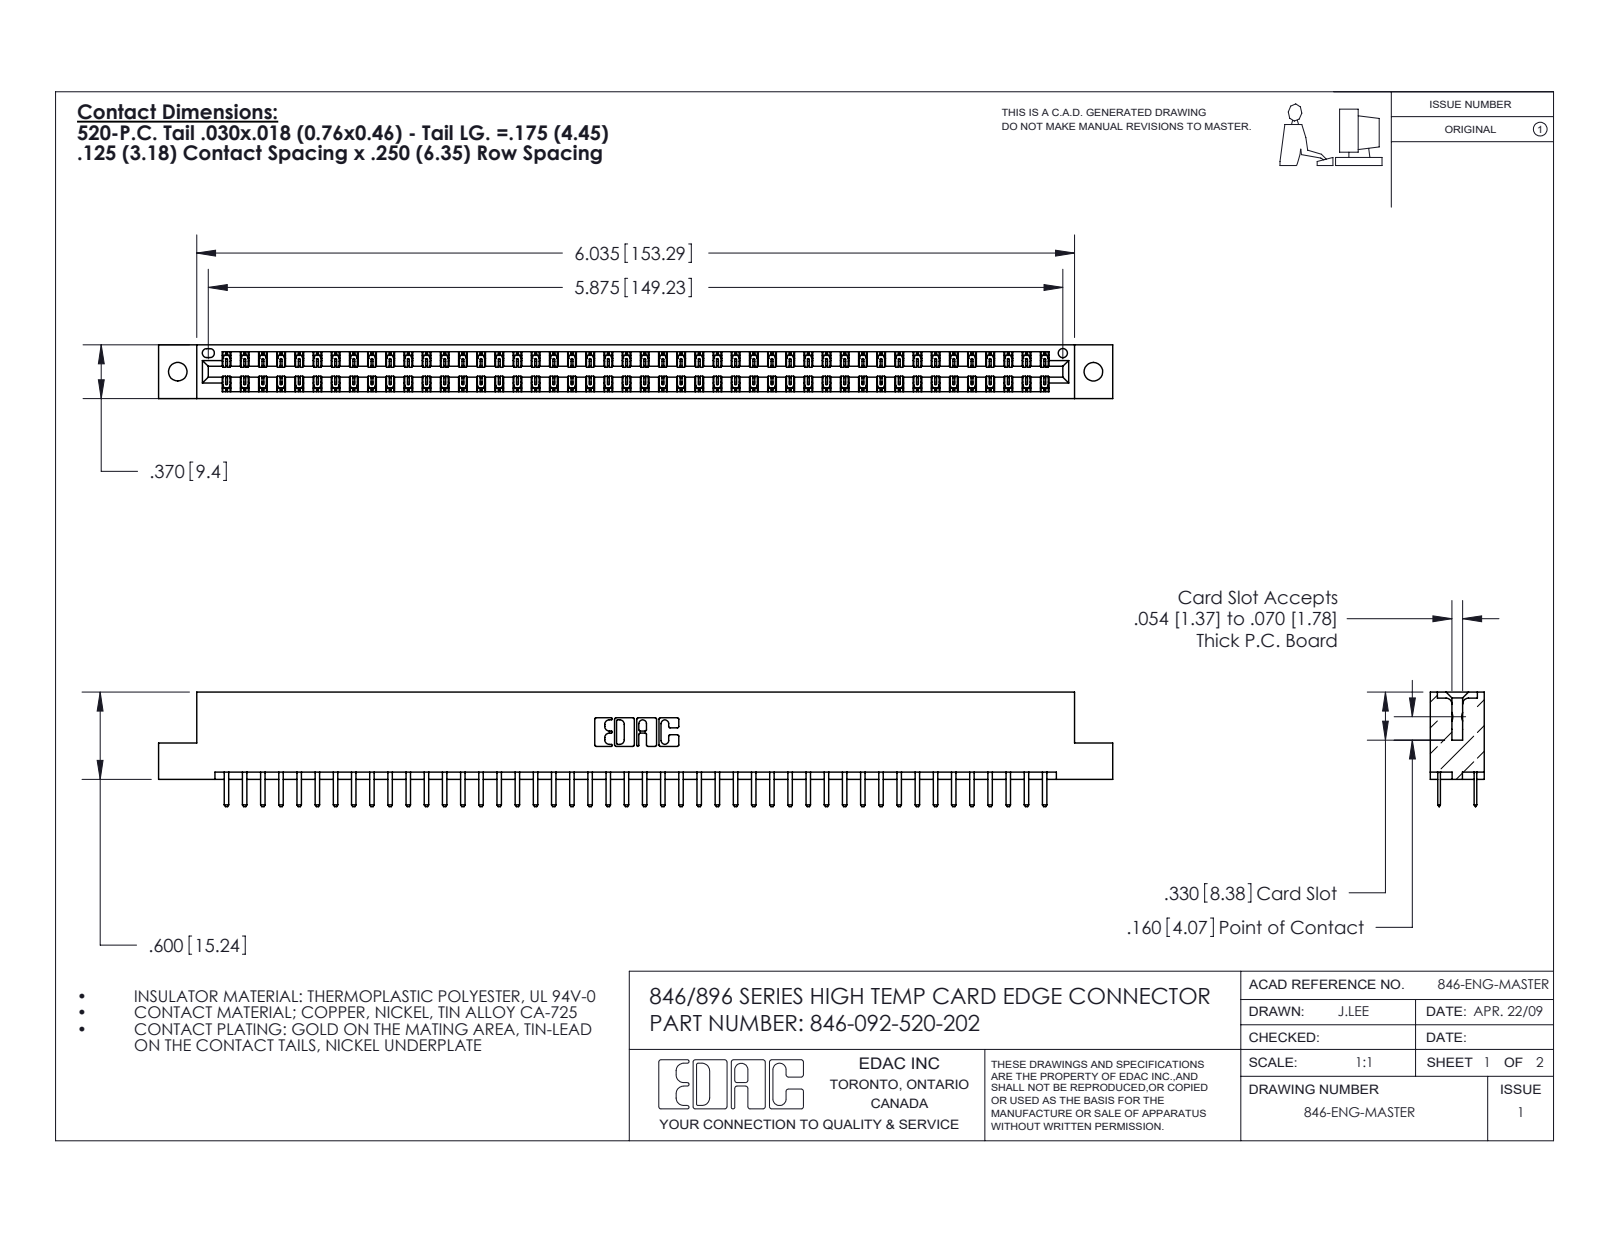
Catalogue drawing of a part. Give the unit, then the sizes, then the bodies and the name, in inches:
Units: inches
Overall size (bounding box): 6.56 × 0.788 × 0.37
Round holes (diameter × count): ⌀0.128 ×2, ⌀0.064 ×1
Partial cylindrical surfaces — rounded edges, fillets, slot ends (radius × count): R0.006 ×138, R0.01 ×96, R0.01 ×22, R0.007 ×6, R0.031 ×6, R0.026 ×3, R0.014 ×2, R0.022 ×2
Main face-to-face distances: 0.048, 0.322, 0.25, 0.37, 0.275, 0.072, 0.298, 0.025, 0.148, 0.222
Hole centre spacings: 0.246, 6.086, 6.295
Volume: 0.989 in³ · Surface area: 34.05 in²
Bodies: 93 solids, 5274 faces (3480 planar, 1794 cylindrical, 0 other)
Part name (STEP PRODUCT): 345-292-001_345-293-120; 346-092-520-202; 346 Part_Flush Mounting Lugs - 0.128 Dia
STEP written by: SolidWorks 2016 (CONFIG_CONTROL_DESIGN)
